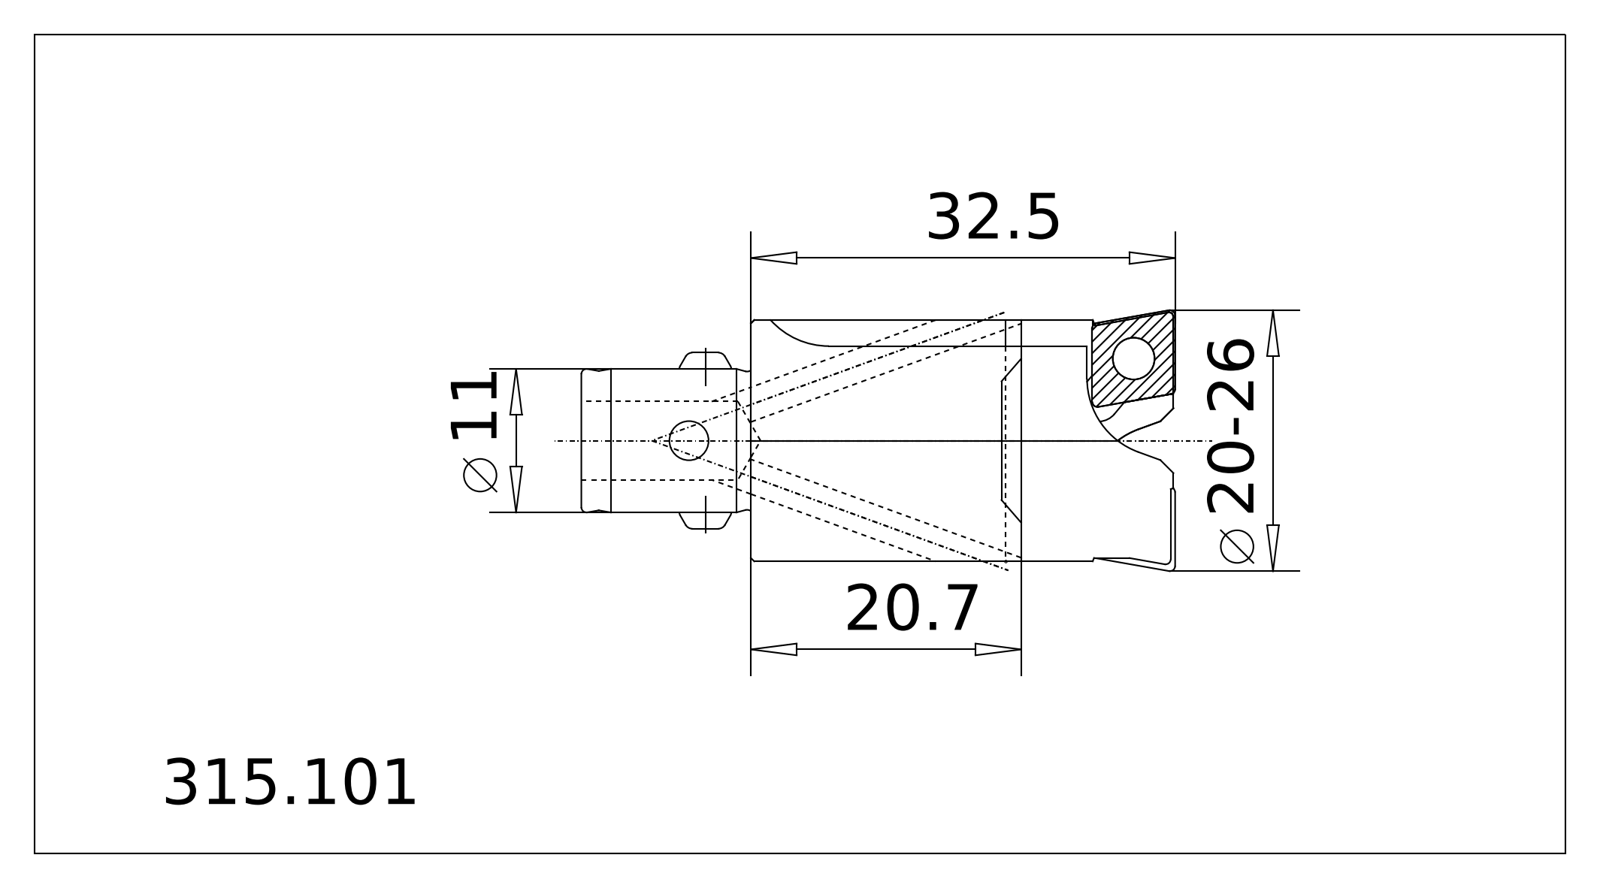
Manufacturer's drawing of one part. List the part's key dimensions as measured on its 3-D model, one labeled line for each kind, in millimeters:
Part name (STEP PRODUCT): 315.101 Kaiser TWN 20-26(31) X CK1|315.160 Kaiser ETL M4_4.15 X 19_Standard;NONE; 315.101 Kaiser TWN 20-26(31) X CK1|315.135 Kaiser TW 20-31 X CK1B_Standard;NONE; 315.101 Kaiser TWN 20-26(31) X CK1|691.501 Kaiser ETL �4 X 13K_Standard|691.521 Mitnehmerbolzen_Standard;NONE; 315.101 Kaiser TWN 20-26(31) X CK1|691.501 Kaiser ETL �4 X 13K_Standard|692.270 O-Ring_Standard;NONE
STEP written by: ACIS (automotive_design)
Units: millimetres
Bodies: 7 solids, 233 faces (59 planar, 68 cylindrical, 106 other)
Overall size (bounding box): 43.7 × 18.5 × 18.5
Volume: 6 303 mm³ · Surface area: 4 377 mm²
Round holes (diameter × count): ⌀3 ×3, ⌀4 ×3, ⌀2.5 ×2, ⌀3.3 ×2, ⌀4.2 ×2, ⌀6 ×1
Round bosses / shafts (diameter × count): ⌀7 ×2, ⌀4.15 ×2, ⌀3.65 ×2, ⌀2.9 ×2, ⌀18.5 ×1, ⌀11 ×1, ⌀3.94 ×1, ⌀2.3 ×1
Partial cylindrical surfaces — rounded edges, fillets, slot ends (radius × count): R6 ×2
Main face-to-face distances: 20.7, 13, 19.5, 1.2, 14.5, 33.7, 32.5, 10, 11.2, 30.7
Hole centre spacings: 5, 10
